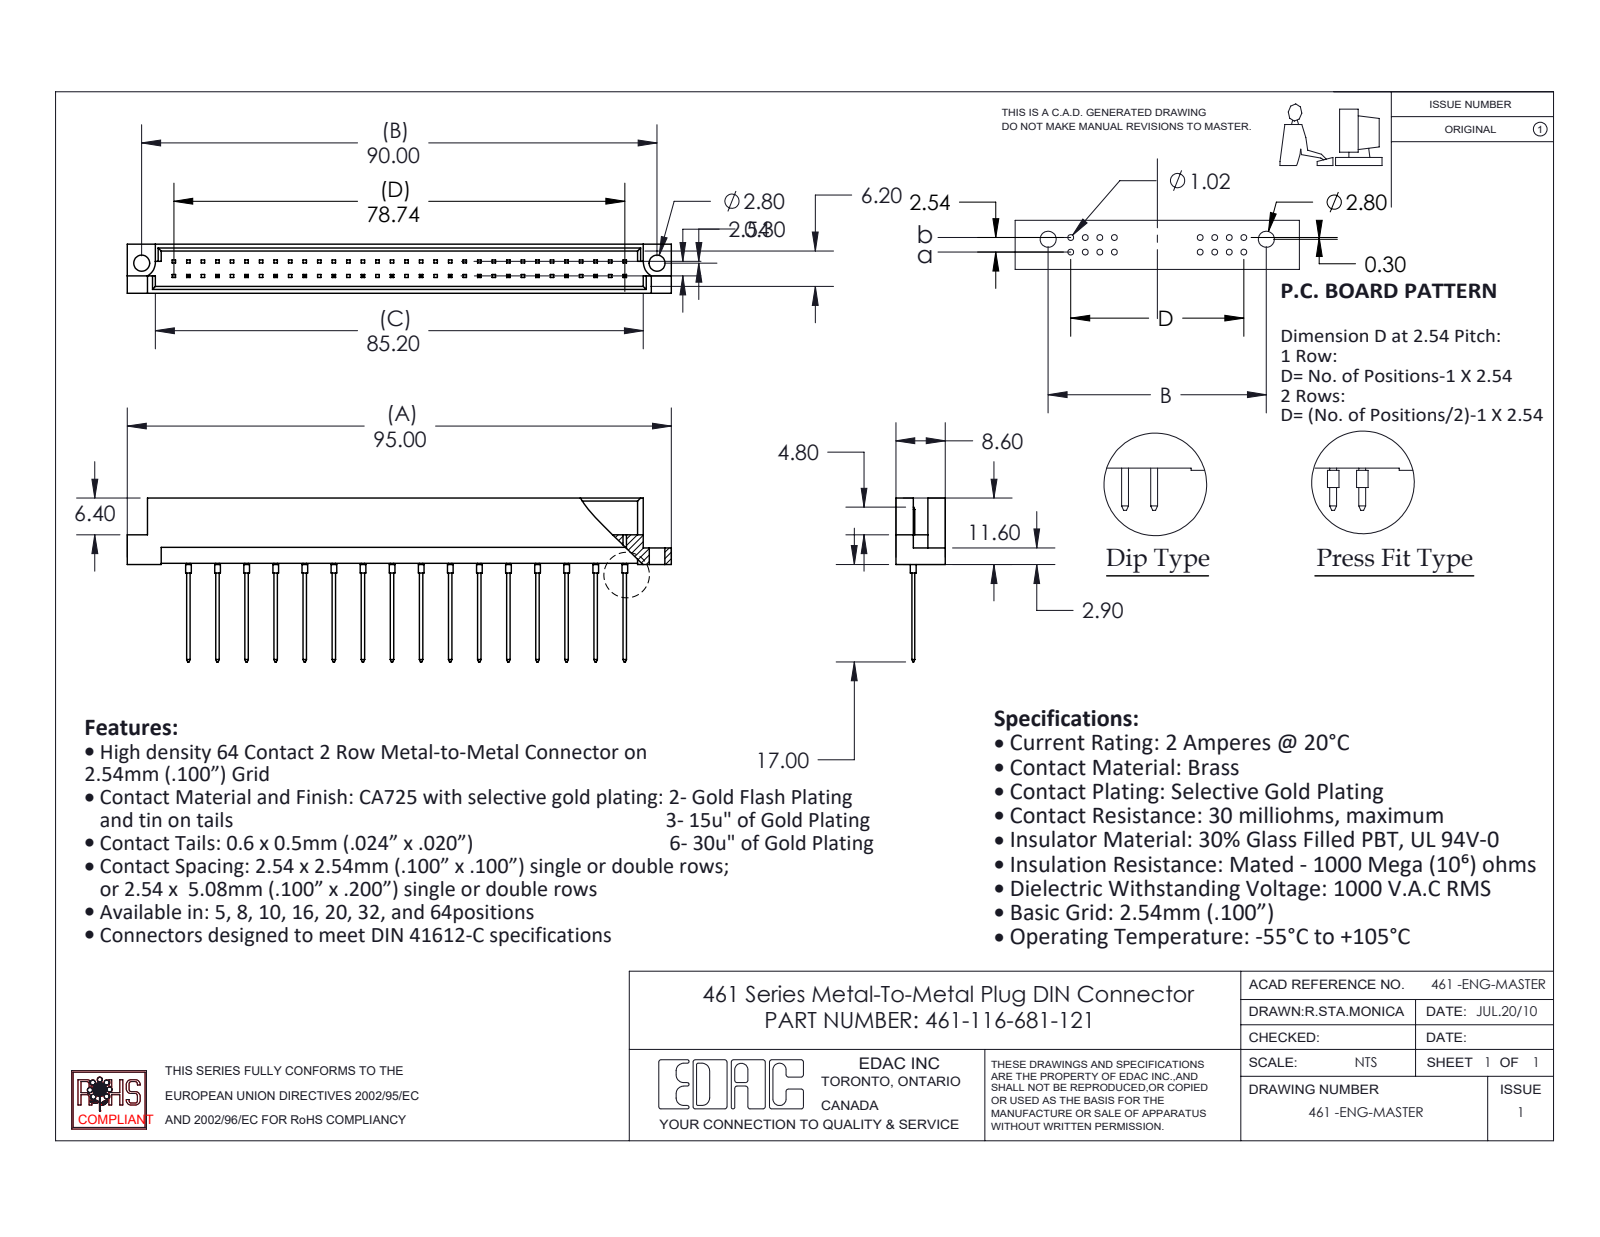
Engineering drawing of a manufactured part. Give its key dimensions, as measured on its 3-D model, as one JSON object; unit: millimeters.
{"part_name": "461-116-681-221; 461 Part_64; 461-290_81", "step_written_by": "SolidWorks 2020 (CONFIG_CONTROL_DESIGN)", "units": "millimeters", "bodies": {"solids": 17, "faces": 657, "planar": 618, "cylindrical": 39, "other": 0}, "overall_size": [95, 28.6, 8.6], "volume_mm3": 4796, "surface_area_mm2": 6654, "round_holes": [[2.8, 2]], "round_bosses_or_shafts": [[1, 16]], "partial_cylinders_radius": [[2.8, 2]], "face_to_face_distances": [1.2, 7.4, 8.6, 6.2, 5, 3.28, 5.32, 2.08, 4.12, 2.78], "hole_center_spacings": [90]}
